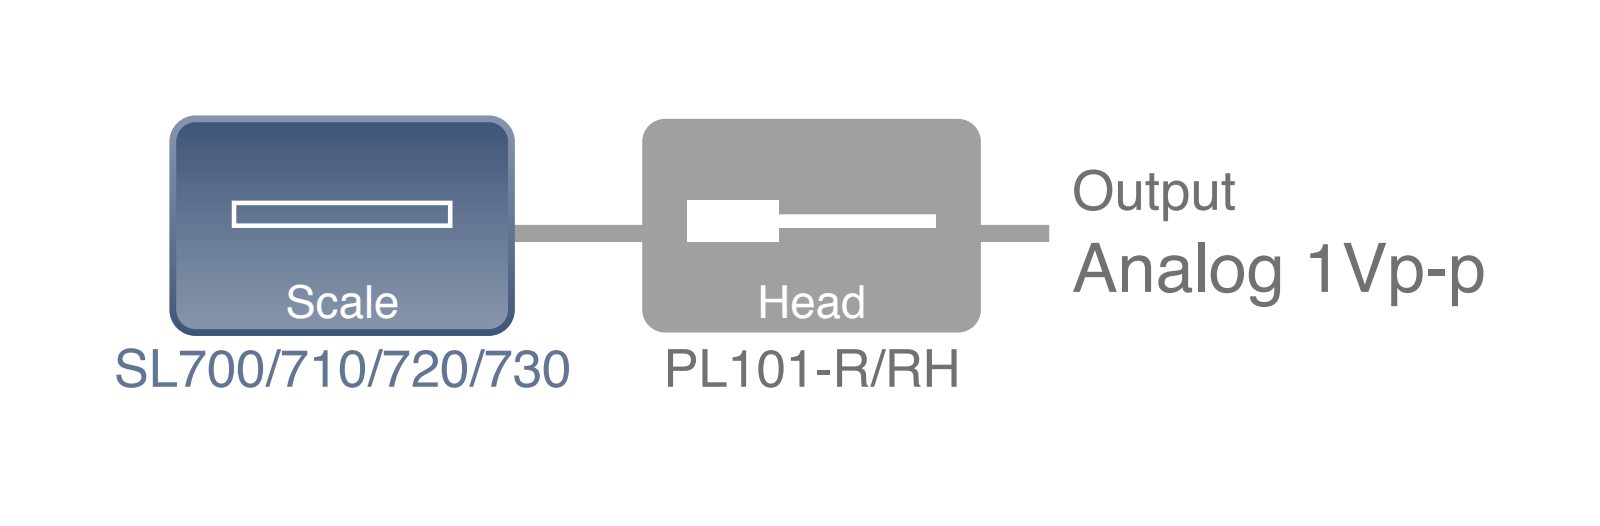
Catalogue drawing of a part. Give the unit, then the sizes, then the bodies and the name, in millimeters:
Units: millimetres
Overall size (bounding box): 70 × 25 × 12
Round holes (diameter × count): ⌀2.8 ×4, ⌀5.4 ×4, ⌀1.57 ×2, ⌀2 ×2, ⌀2.46 ×2, ⌀4.6 ×1
Round bosses / shafts (diameter × count): ⌀5.2 ×4, ⌀7 ×1, ⌀4.4 ×1
Partial cylindrical surfaces — rounded edges, fillets, slot ends (radius × count): R0.5 ×30, R0.8 ×8, R1 ×8, R0.2 ×4, R0.4 ×4, R0.9 ×4, R1.2 ×4
Main face-to-face distances: 12, 25, 11.7, 48, 24.8, 11.9, 11.6, 24.6, 47.8, 0.6
Hole centre spacings: 3.08, 7.08, 10.12, 16.02, 17.4, 40.2, 43.8, 13
Volume: 14 320 mm³ · Surface area: 5 105 mm²
Bodies: 1 solid, 290 faces (109 planar, 122 cylindrical, 59 other)
Part name (STEP PRODUCT): PL101_HeadUnit
STEP written by: CATIA V5 STEP AP214 (AUTOMOTIVE_DESIGN)
